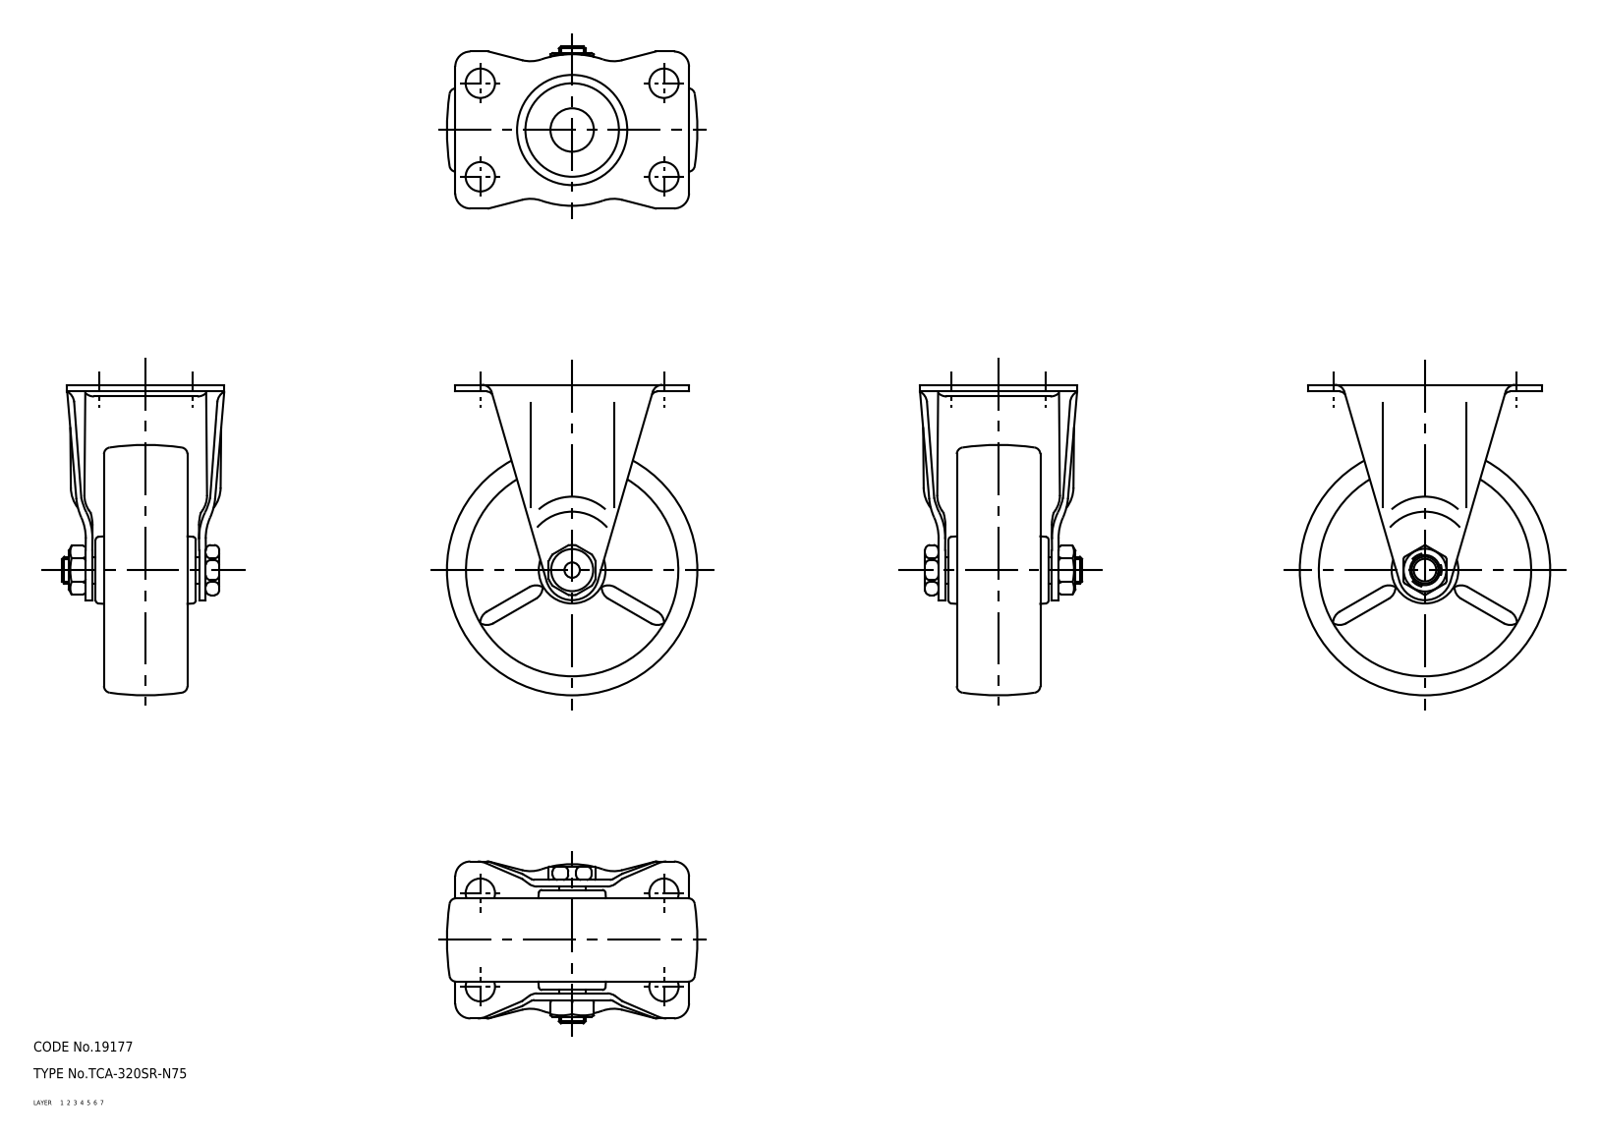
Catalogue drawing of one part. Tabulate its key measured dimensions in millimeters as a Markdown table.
| quantity | value |
| --- | --- |
| part name | wheel; axle; 320SR_N75_8413_36 |
| STEP written by | CADfix (AUTOMOTIVE_DESIGN) |
| units | millimeters |
| bodies | 3 solids, 333 faces (0 planar, 0 cylindrical, 333 other) |
| overall size | 93 × 75 × 48.5 |
| volume | 98 073 mm³ |
| surface area | 34 020 mm² |
